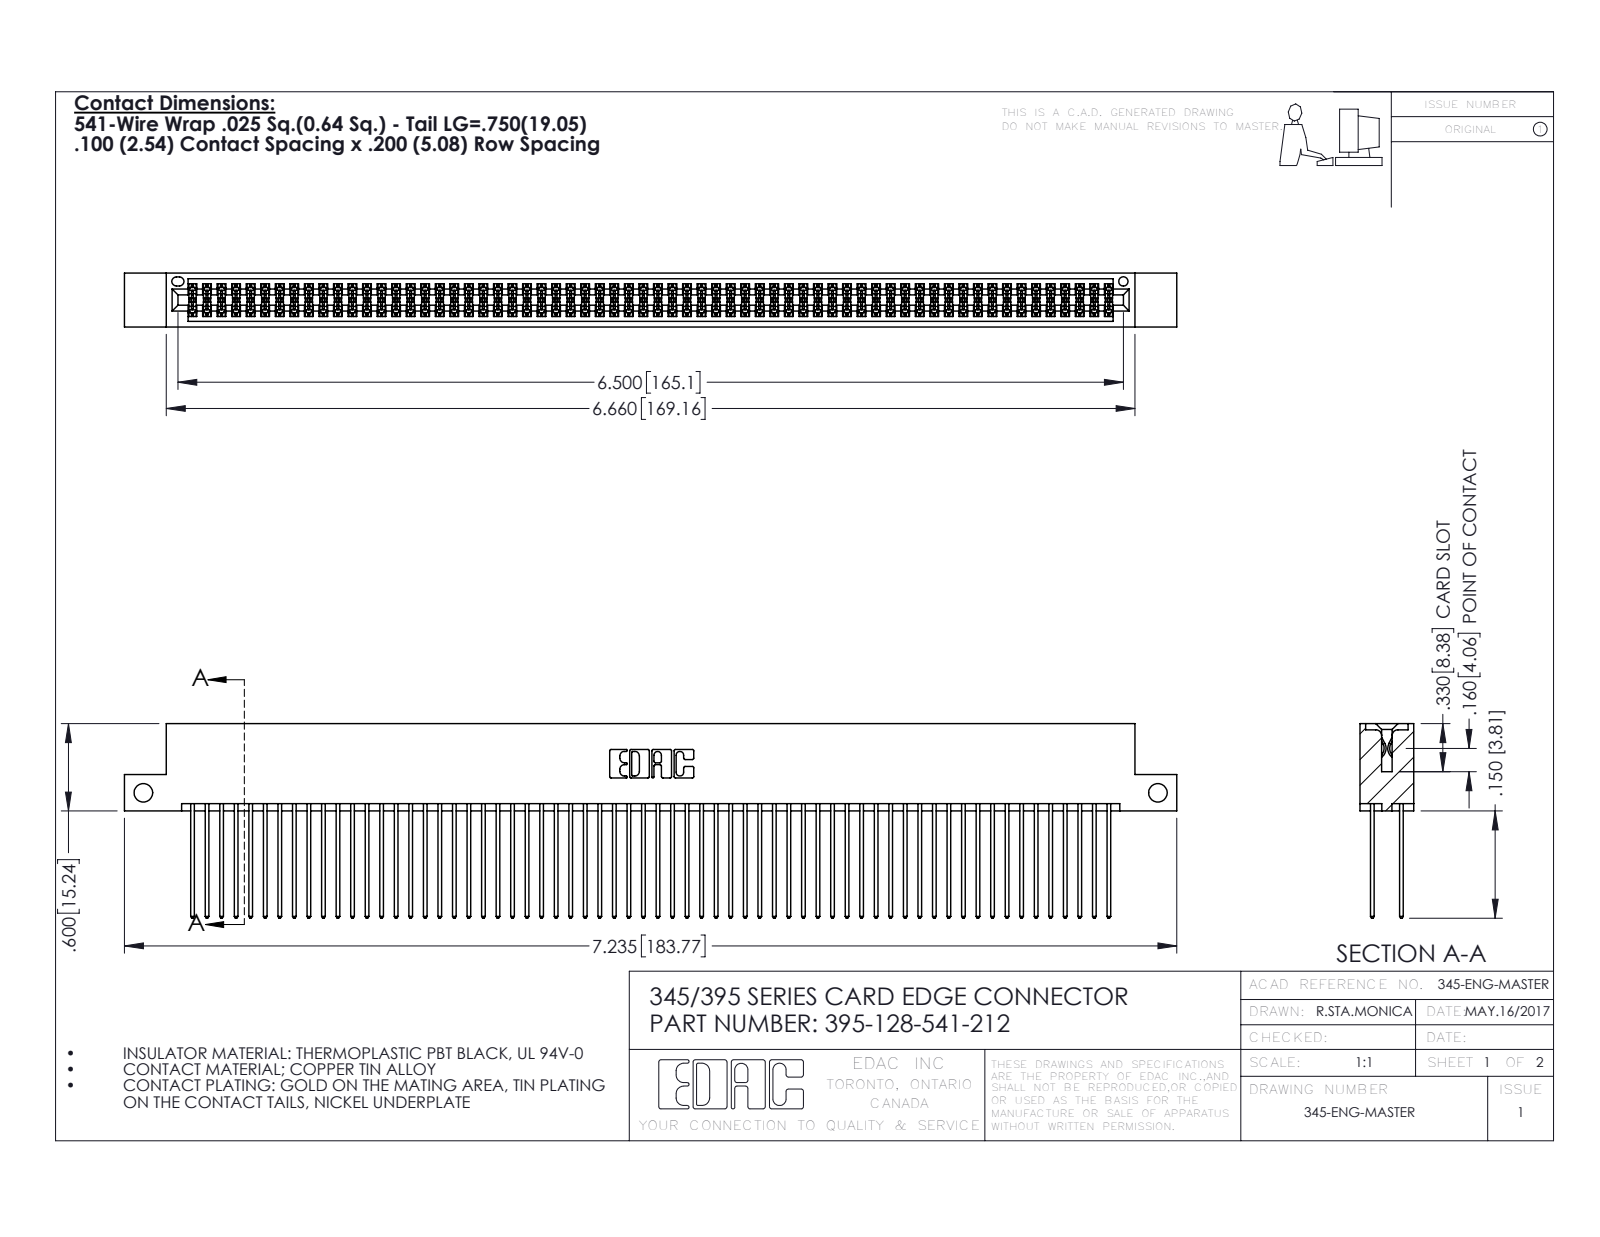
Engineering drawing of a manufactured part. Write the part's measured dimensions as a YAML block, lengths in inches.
part_name: "395-128-541-212; 345 Part_Flush Mounting Lugs - Side Mount; 345-292-001_345-293-141"
step_written_by: "SolidWorks 2016 (CONFIG_CONTROL_DESIGN)"
units: inches
bodies: {solids: 129, faces: 6526, planar: 4304, cylindrical: 2222, other: 0}
overall_size: [7.235, 1.337, 0.37]
volume: 1.141
surface_area: 48.65
round_holes:
  - {diameter: 0.128, count: 2}
  - {diameter: 0.064, count: 1}
partial_cylinders:
  - {radius: 0.006, count: 192}
  - {radius: 0.01, count: 128}
  - {radius: 0.01, count: 22}
  - {radius: 0.007, count: 6}
  - {radius: 0.031, count: 6}
  - {radius: 0.026, count: 3}
  - {radius: 0.014, count: 2}
  - {radius: 0.019, count: 2}
face_to_face_distances: [0.298, 0.072, 0.2, 0.098, 0.272, 0.025, 0.225, 0.37, 0.175, 0.149]
hole_center_spacings: [6.975]
